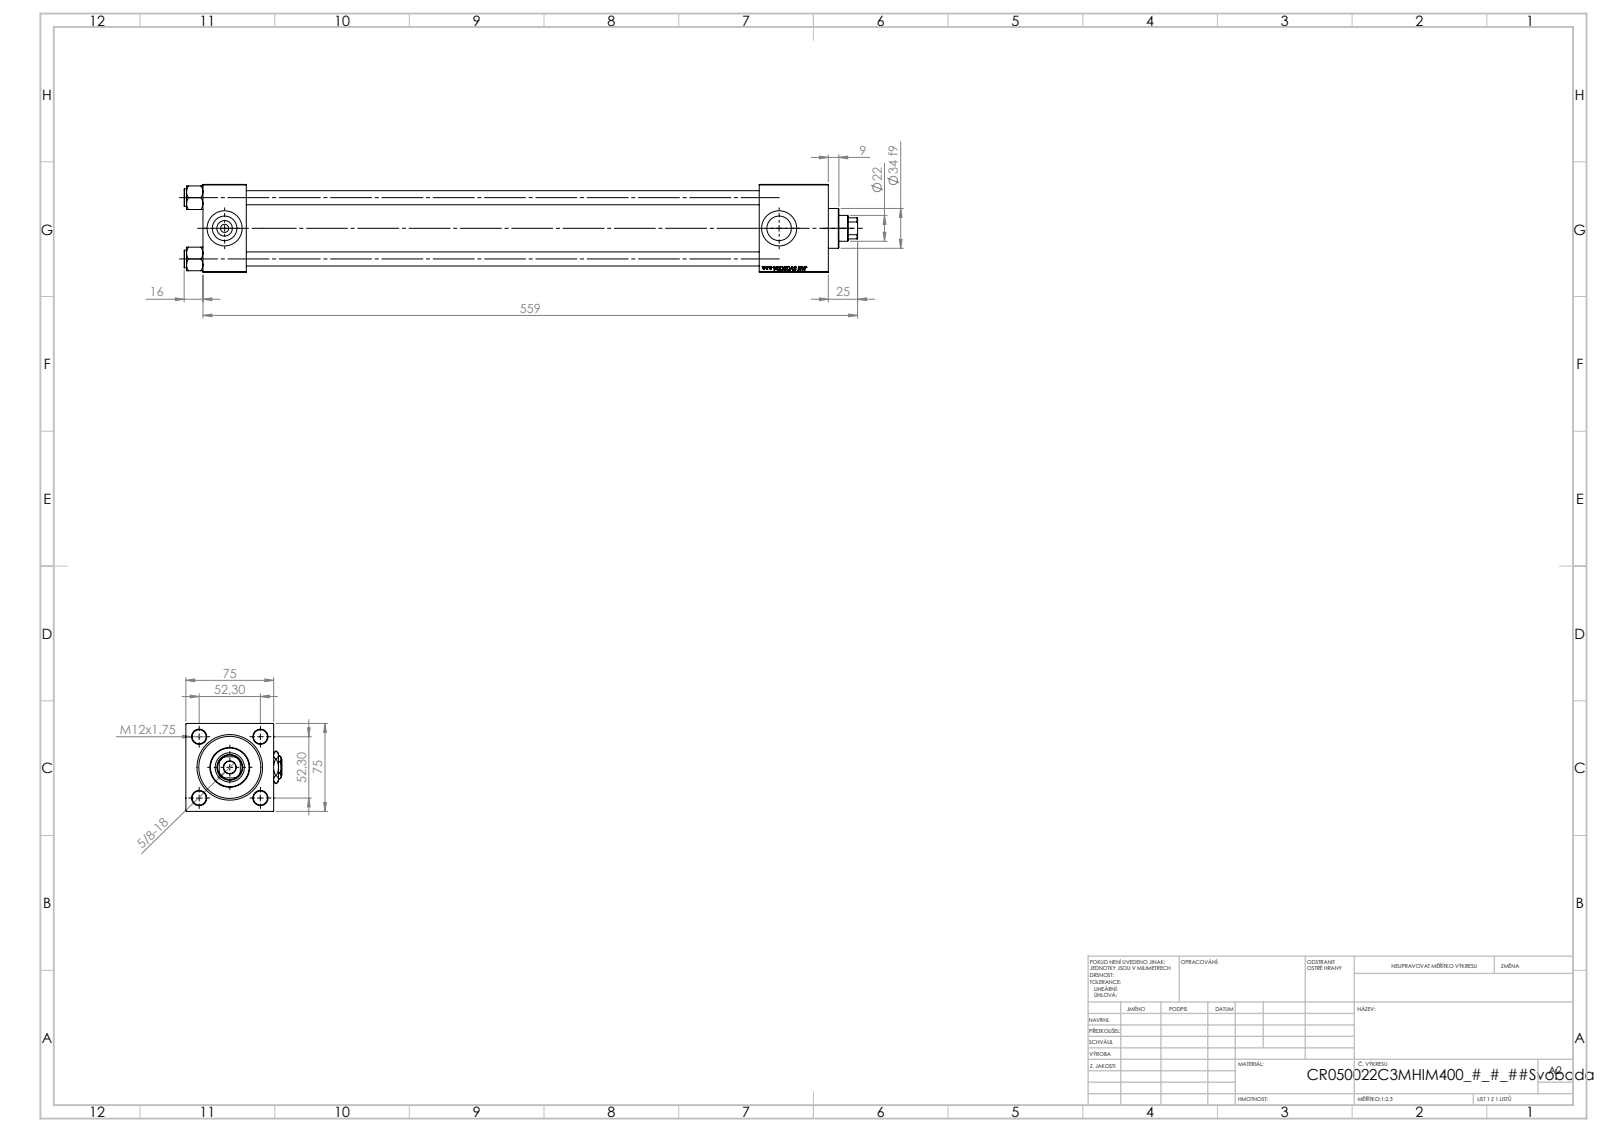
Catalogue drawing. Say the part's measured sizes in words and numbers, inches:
The part is named "Zatka_pro_OIL_PORT; V215_VC_A; V215CR_VCP_C; NUT_M5_C (+2 more)". Its 3-D file was written by "SolidWorks 2019 (CONFIG_CONTROL_DESIGN)". It is 13 solids with 1249 faces: 573 planar, 98 cylindrical and 578 other. Overall it measures 22.638 by 3.239 by 2.953 inches. Its volume is 70.67 cubic inches and its surface area 560.9 square inches. Round holes: 4 of diameter 0.472, 2 of diameter 0.276, 2 of diameter 0.825, 2 of diameter 1.181, 1 of diameter 0.413, 1 of diameter 0.866, 1 of diameter 0.984, 1 of diameter 1.614, 1 of diameter 1.969, 1 of diameter 2.087. Round bosses or shafts: 4 of diameter 0.591, 1 of diameter 2.205, 1 of diameter 1.339. Partial cylindrical surfaces (rounded edges, fillets, slot ends): 1 of radius 0.413. The main face-to-face distances are 2.953, 1.457, 21.024, 19.567, 18.701, 17.244, 2.323, 19.894, 18.437, 1.193. The hole center spacings are 1.456, 2.059, 2.912, 18.642.
